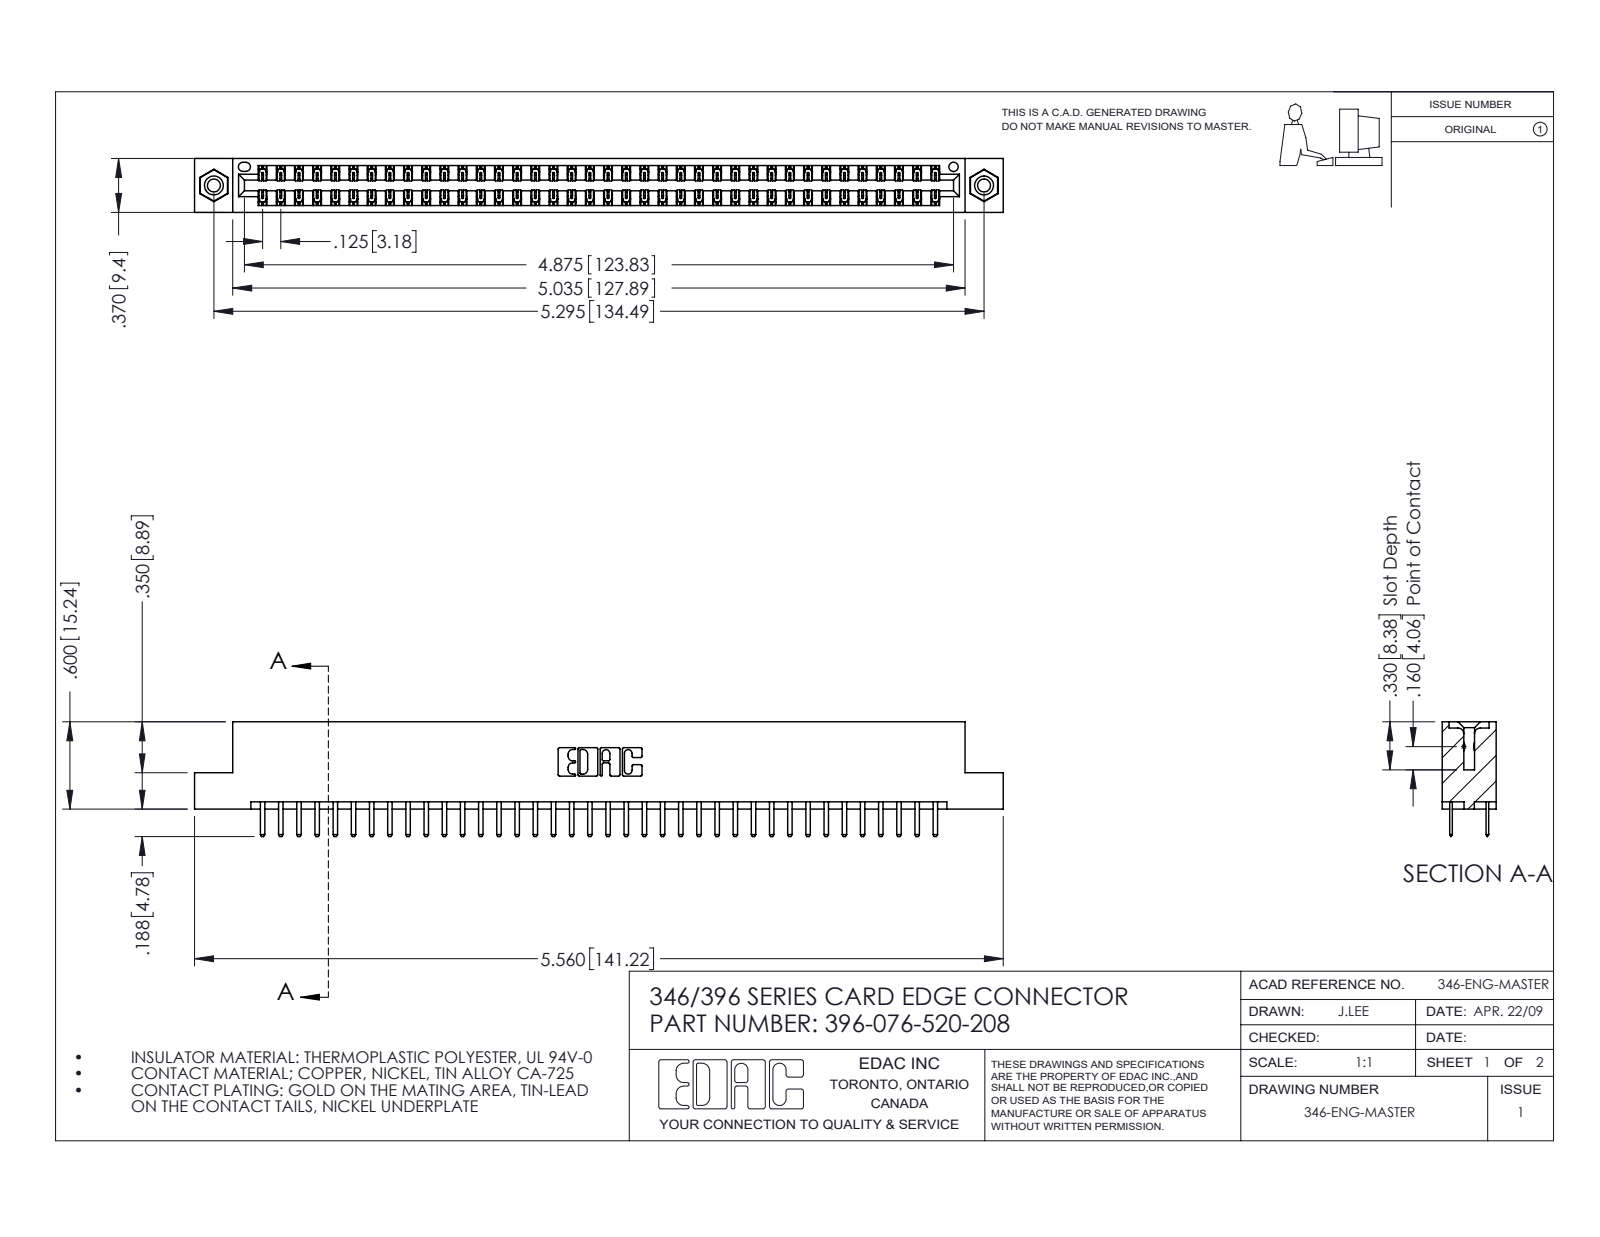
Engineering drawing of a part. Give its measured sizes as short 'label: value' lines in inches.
name: 345-292-001_345-293-120; 396-076-520-208; 345-250-001_345-250-003-102; 346 Part_Flush Mounting Lugs - 0.156 Dia-TI
written by: SolidWorks 2016 (CONFIG_CONTROL_DESIGN)
unit: in
bodies: 79 solids, 4438 faces (2920 planar, 1502 cylindrical, 16 other)
size: 5.56 × 0.788 × 0.37
volume: 0.836 in³; area: 29 in²
holes: 2× ⌀0.089, 2× ⌀0.125, 2× ⌀0.156, 1× ⌀0.064
bosses: 2× ⌀0.155
rounds: 114× R0.006, 80× R0.01, 22× R0.01, 6× R0.007, 6× R0.031, 3× R0.026, 2× R0.014, 2× R0.022
face distances: 0.048, 0.322, 0.25, 0.37, 0.275, 0.072, 0.298, 0.025, 0.148, 0.222
hole spacings: 0.246, 5.086, 5.295
